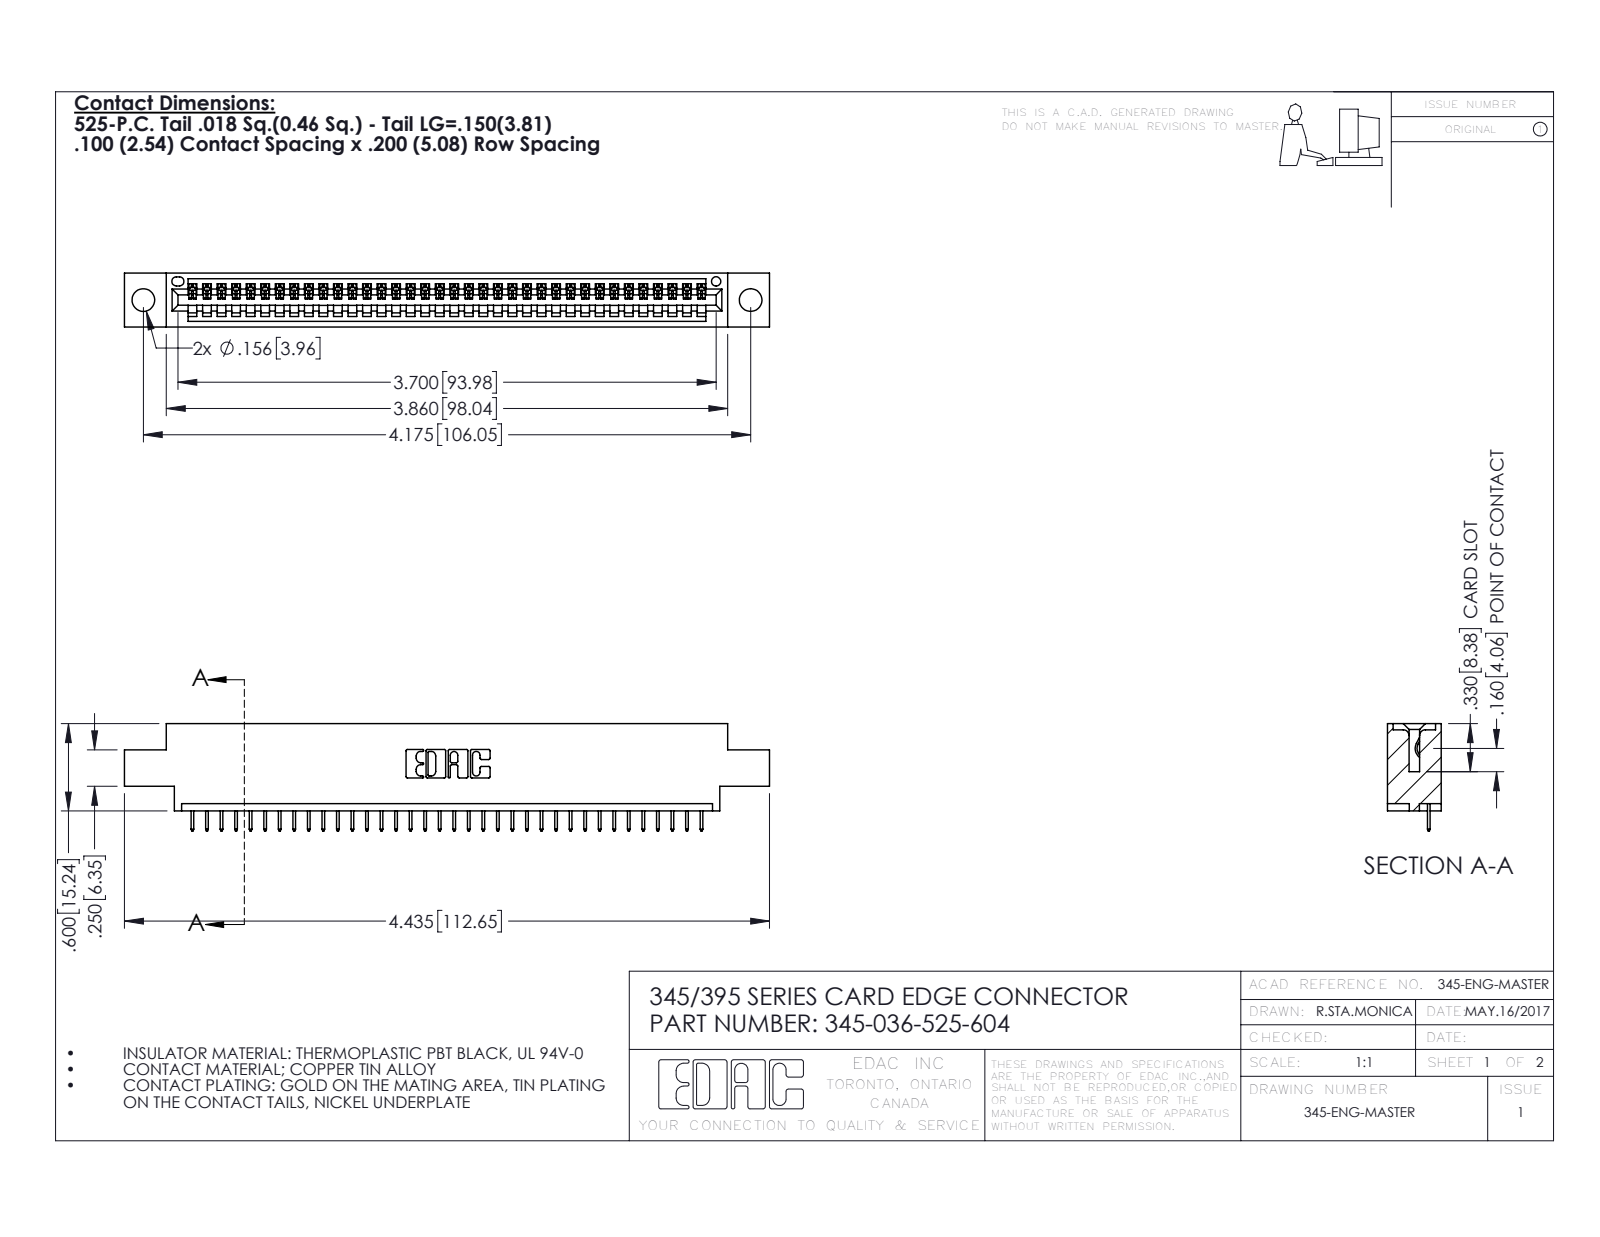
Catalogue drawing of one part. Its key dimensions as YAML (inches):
part_name: "345-292-001_345-293-125; 345 Part_0.170 Offset - 0.156 Dia-TH; 345-036-525-604"
step_written_by: "SolidWorks 2020 (CONFIG_CONTROL_DESIGN)"
units: inches
bodies: {solids: 37, faces: 2362, planar: 1740, cylindrical: 622, other: 0}
overall_size: [4.435, 0.737, 0.37]
volume: 0.629
surface_area: 20.23
round_holes:
  - {diameter: 0.156, count: 2}
  - {diameter: 0.064, count: 1}
partial_cylinders:
  - {radius: 0.006, count: 72}
  - {radius: 0.01, count: 22}
  - {radius: 0.007, count: 6}
  - {radius: 0.031, count: 6}
  - {radius: 0.026, count: 3}
  - {radius: 0.031, count: 2}
  - {radius: 0.04, count: 2}
  - {radius: 0.014, count: 1}
face_to_face_distances: [0.072, 0.298, 0.37, 0.2, 0.098, 0.272, 0.025, 0.225, 0.175, 0.072]
hole_center_spacings: [0.27, 3.939, 4.175]
